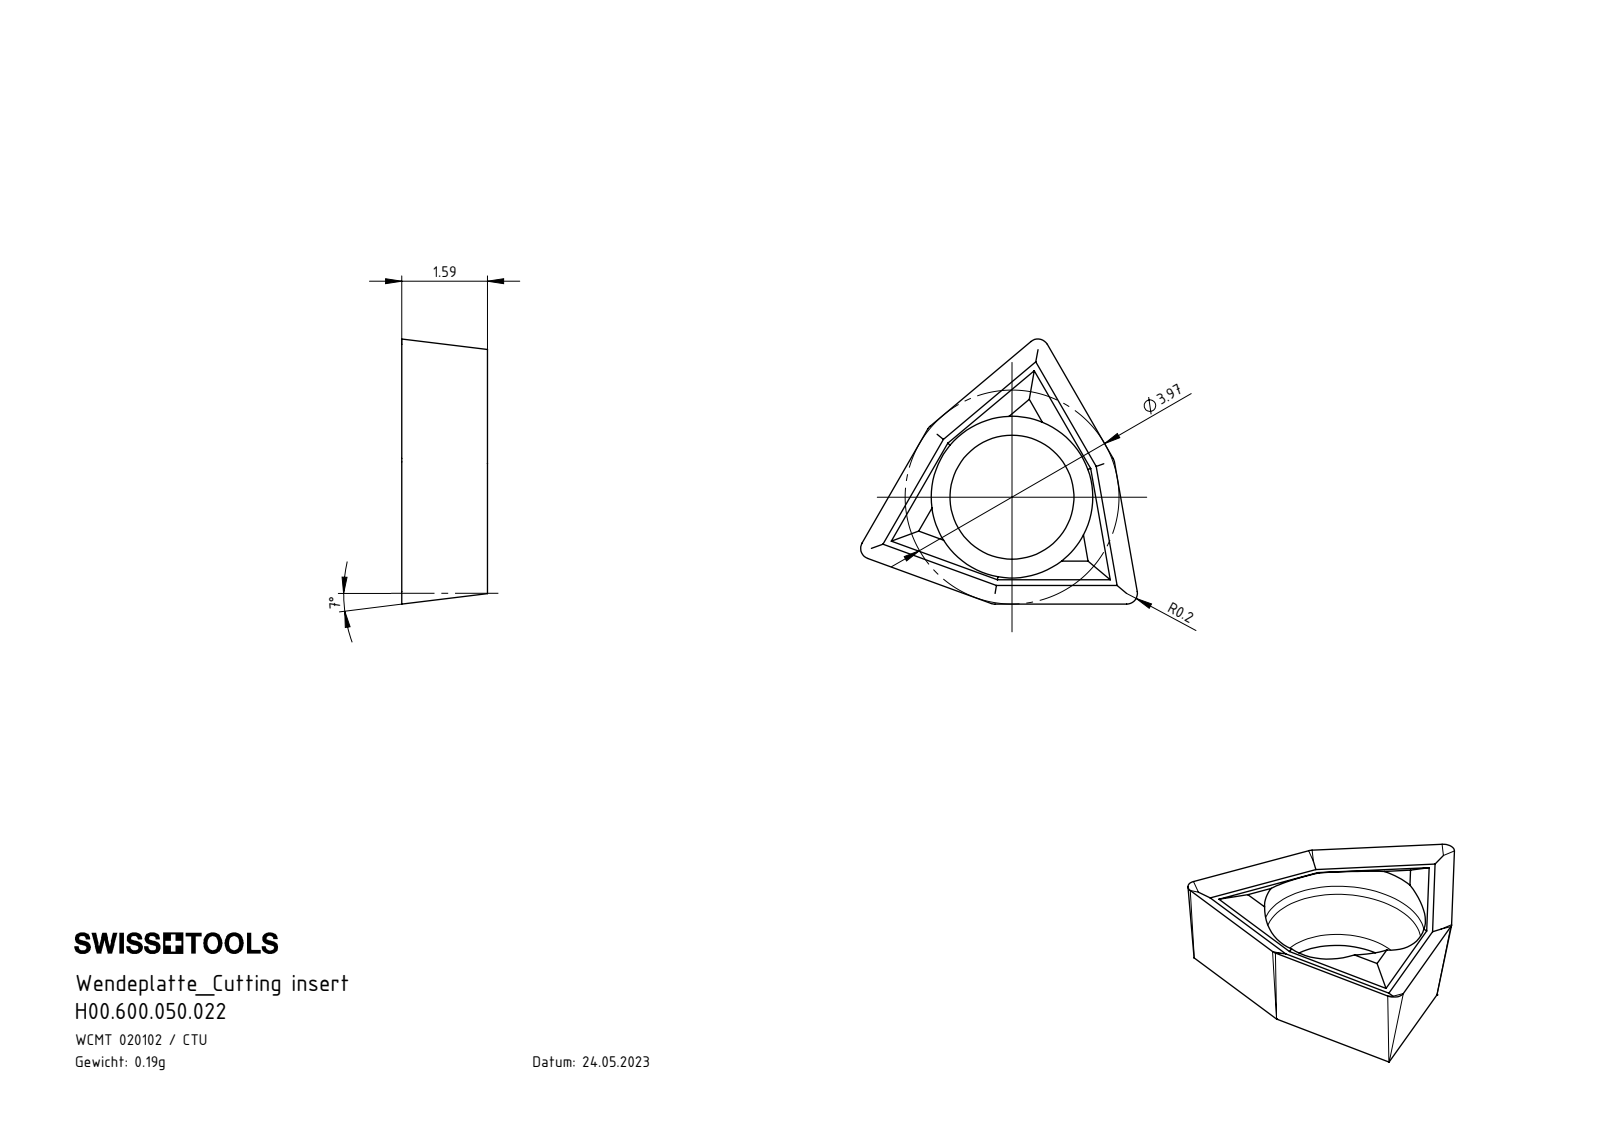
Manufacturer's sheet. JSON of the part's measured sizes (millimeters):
{"part_name": "H00.600.050.022", "step_written_by": "SolidWorks 2022 (AUTOMOTIVE_DESIGN)", "units": "millimeters", "bodies": {"solids": 1, "faces": 43, "planar": 23, "cylindrical": 4, "other": 16}, "overall_size": [5.14, 4.92, 1.59], "volume_mm3": 13, "surface_area_mm2": 57, "round_holes": [[2.3, 1], [3, 1]], "face_to_face_distances": [1.39, 1.59]}
